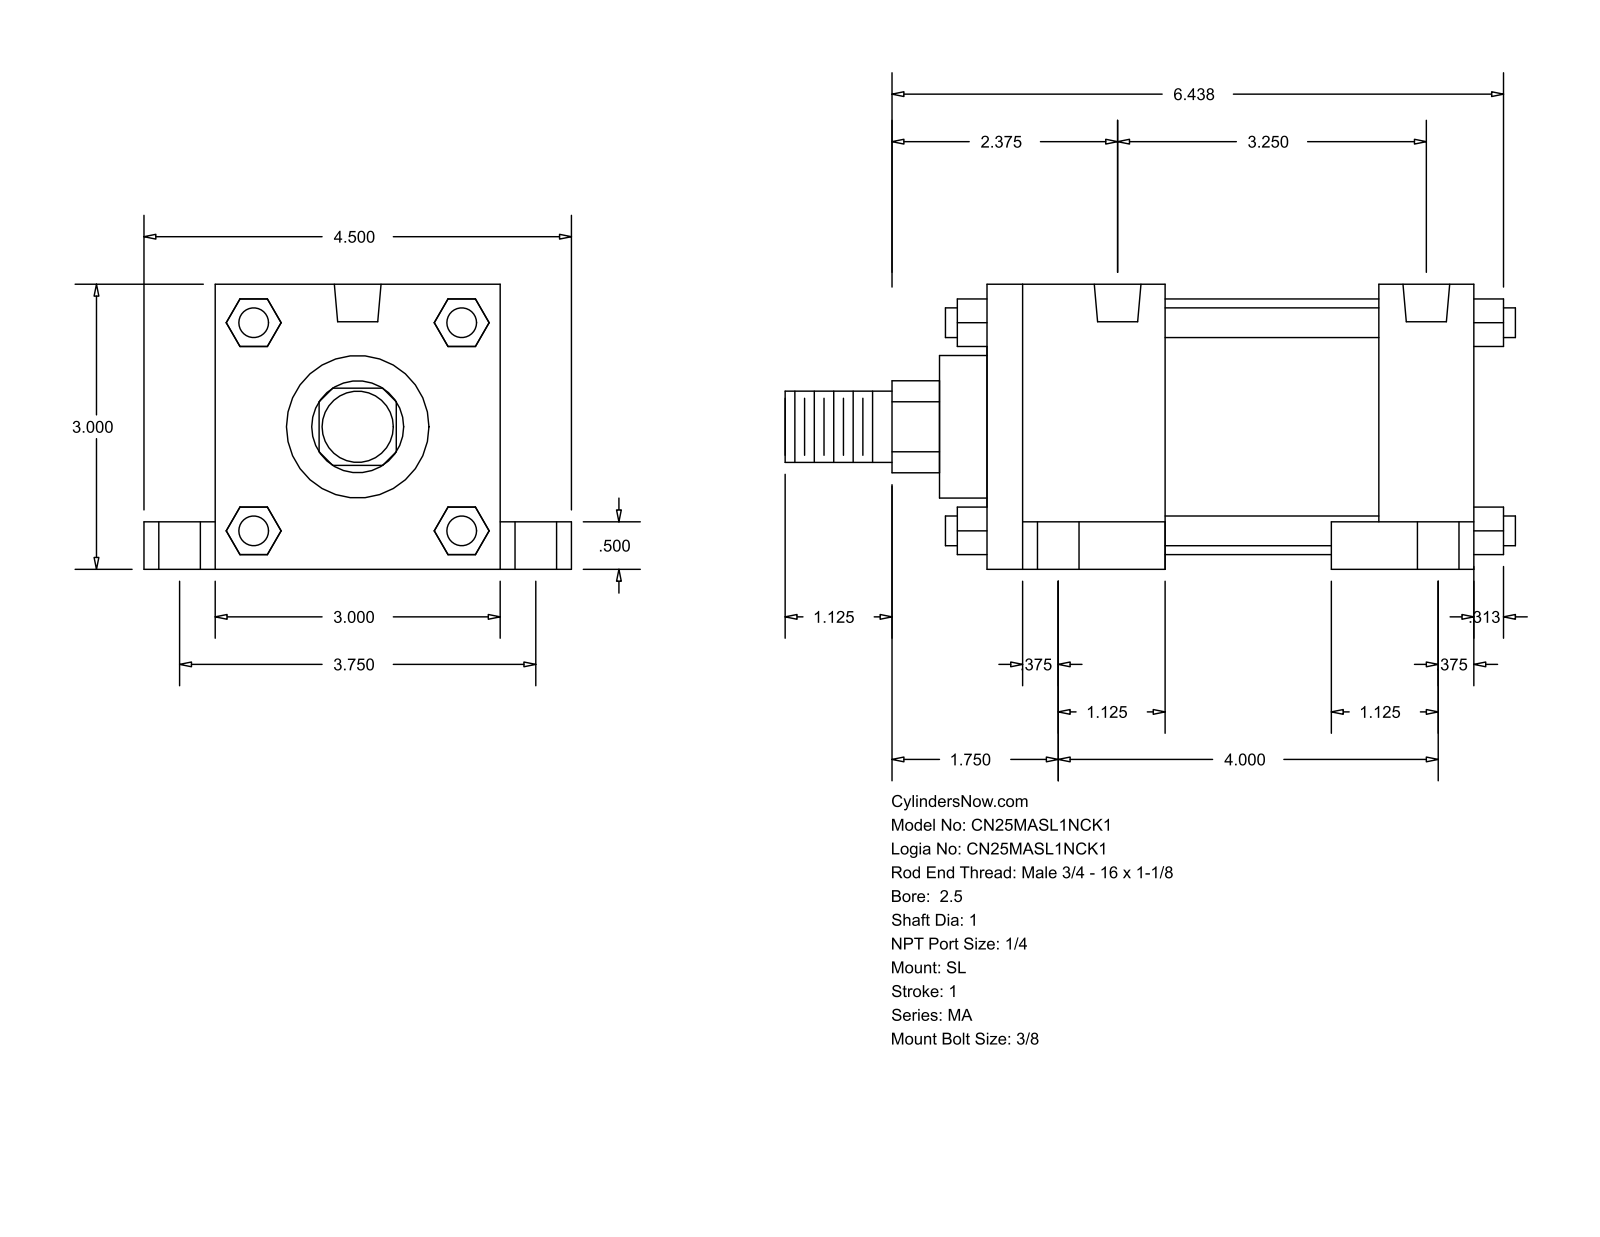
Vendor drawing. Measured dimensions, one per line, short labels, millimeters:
name: MA_SL__0250_1
written by: GSSL Pune (CONFIG_CONTROL_DESIGN)
unit: mm
bodies: 0 solids, 148 faces (112 planar, 36 cylindrical, 0 other)
size: 195.26 × 114.3 × 76.2
holes: 4× ⌀7.94, 4× ⌀11.11, 4× ⌀17.46, 2× ⌀12.49
bosses: 4× ⌀7.94, 1× ⌀68.33, 1× ⌀38.1, 1× ⌀25.4, 1× ⌀19.05
rounds: 1× R12.29
face distances: 76.2, 130.17, 12.7, 57.15, 25.39, 47.63, 82.54, 104.78, 19.05, 95.25
hole spacings: 47.73, 50.2, 82.55, 95.24, 98.06, 101.6, 109.34, 139.26
